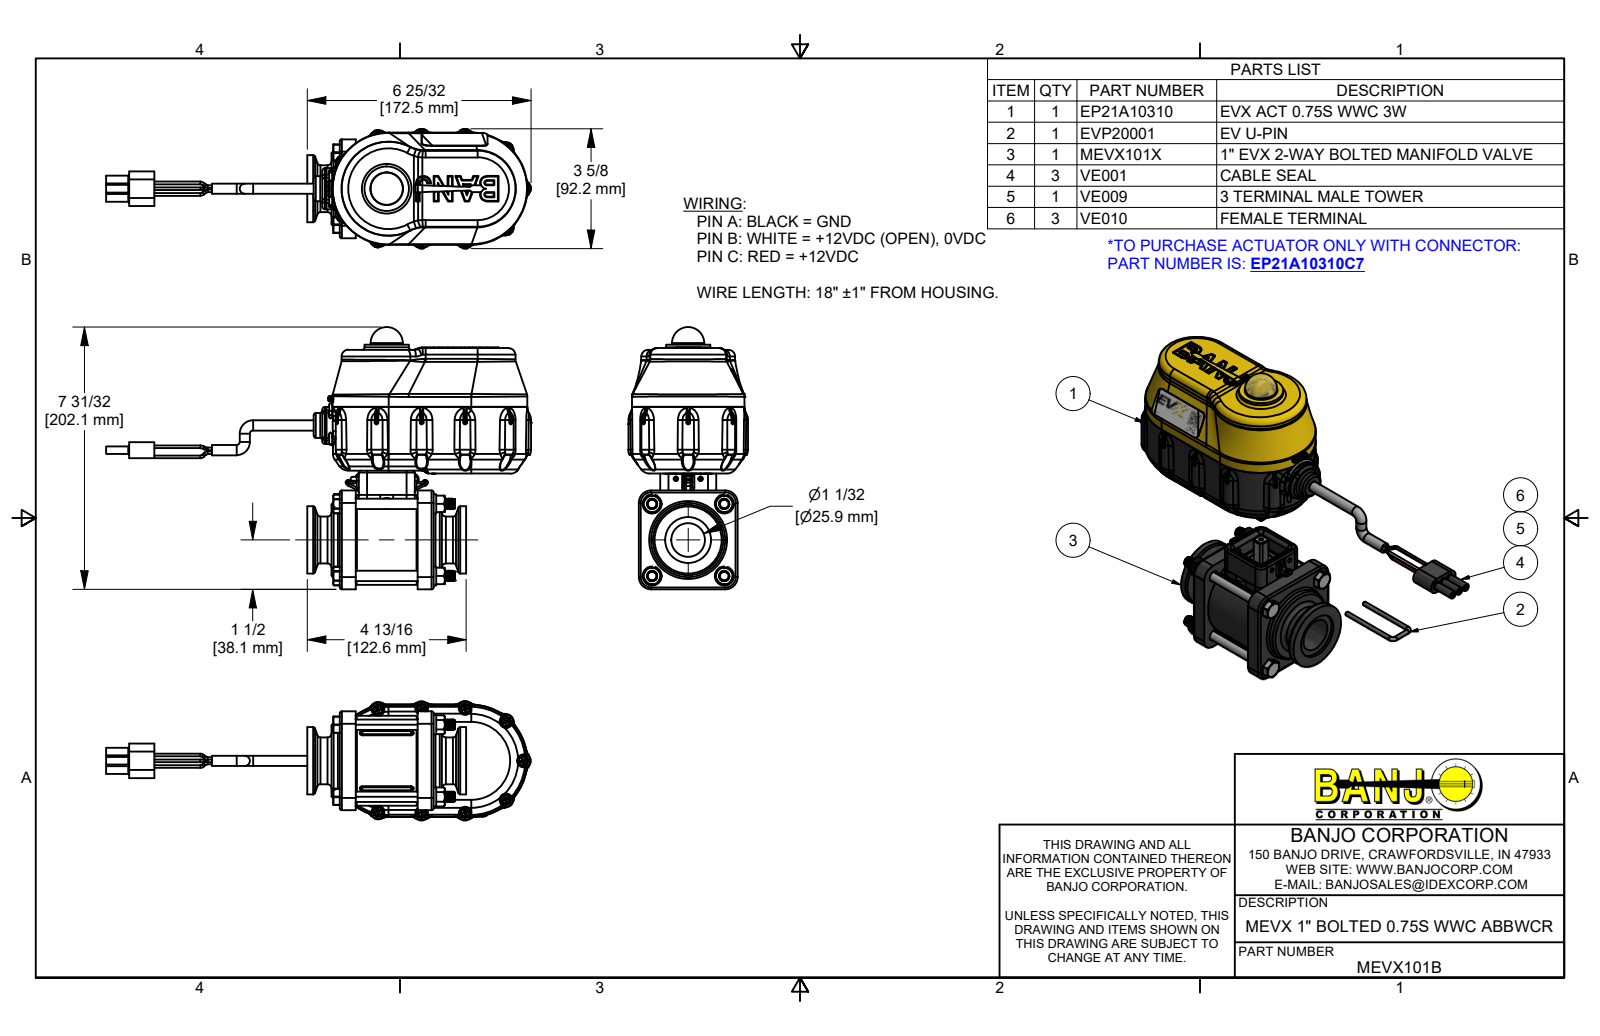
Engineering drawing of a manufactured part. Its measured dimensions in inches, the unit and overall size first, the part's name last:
Units: inches
Overall size (bounding box): 12.901 × 7.957 × 3.63
Round holes (diameter × count): ⌀0.095 ×11, ⌀0.15 ×11, ⌀0.08 ×7, ⌀0.107 ×4, ⌀0.126 ×4, ⌀0.135 ×4, ⌀0.136 ×4, ⌀0.148 ×4, ⌀0.15 ×4, ⌀0.17 ×4, ⌀0.252 ×4, ⌀0.322 ×4
Round bosses / shafts (diameter × count): ⌀0.268 ×60, ⌀0.25 ×17, ⌀0.08 ×15, ⌀0.14 ×11, ⌀0.108 ×11, ⌀0.085 ×11, ⌀0.058 ×6, ⌀0.313 ×5
Partial cylindrical surfaces — rounded edges, fillets, slot ends (radius × count): R0.013 ×180, R0.04 ×145, R0.01 ×84, R0.02 ×72, R0.005 ×53, R0.06 ×42, R0.03 ×38, R0.08 ×28
Main face-to-face distances: 0.1, 2.565, 0.48, 0.211, 0.06, 0.151, 0.055, 2.365, 0.125, 1.896
Hole centre spacings: 0.874, 0.946, 1.547, 1.662, 1.891, 2.188, 2.656, 2.69
Volume: 51.59 in³ · Surface area: 602.1 in²
Bodies: 103 solids, 11465 faces (2883 planar, 3487 cylindrical, 5095 other)
Part name (STEP PRODUCT): MEVX101B; EP21A10310; EP10310; IRF4905 (+8 more)
STEP written by: Autodesk Inventor 2019 (AUTOMOTIVE_DESIGN)
